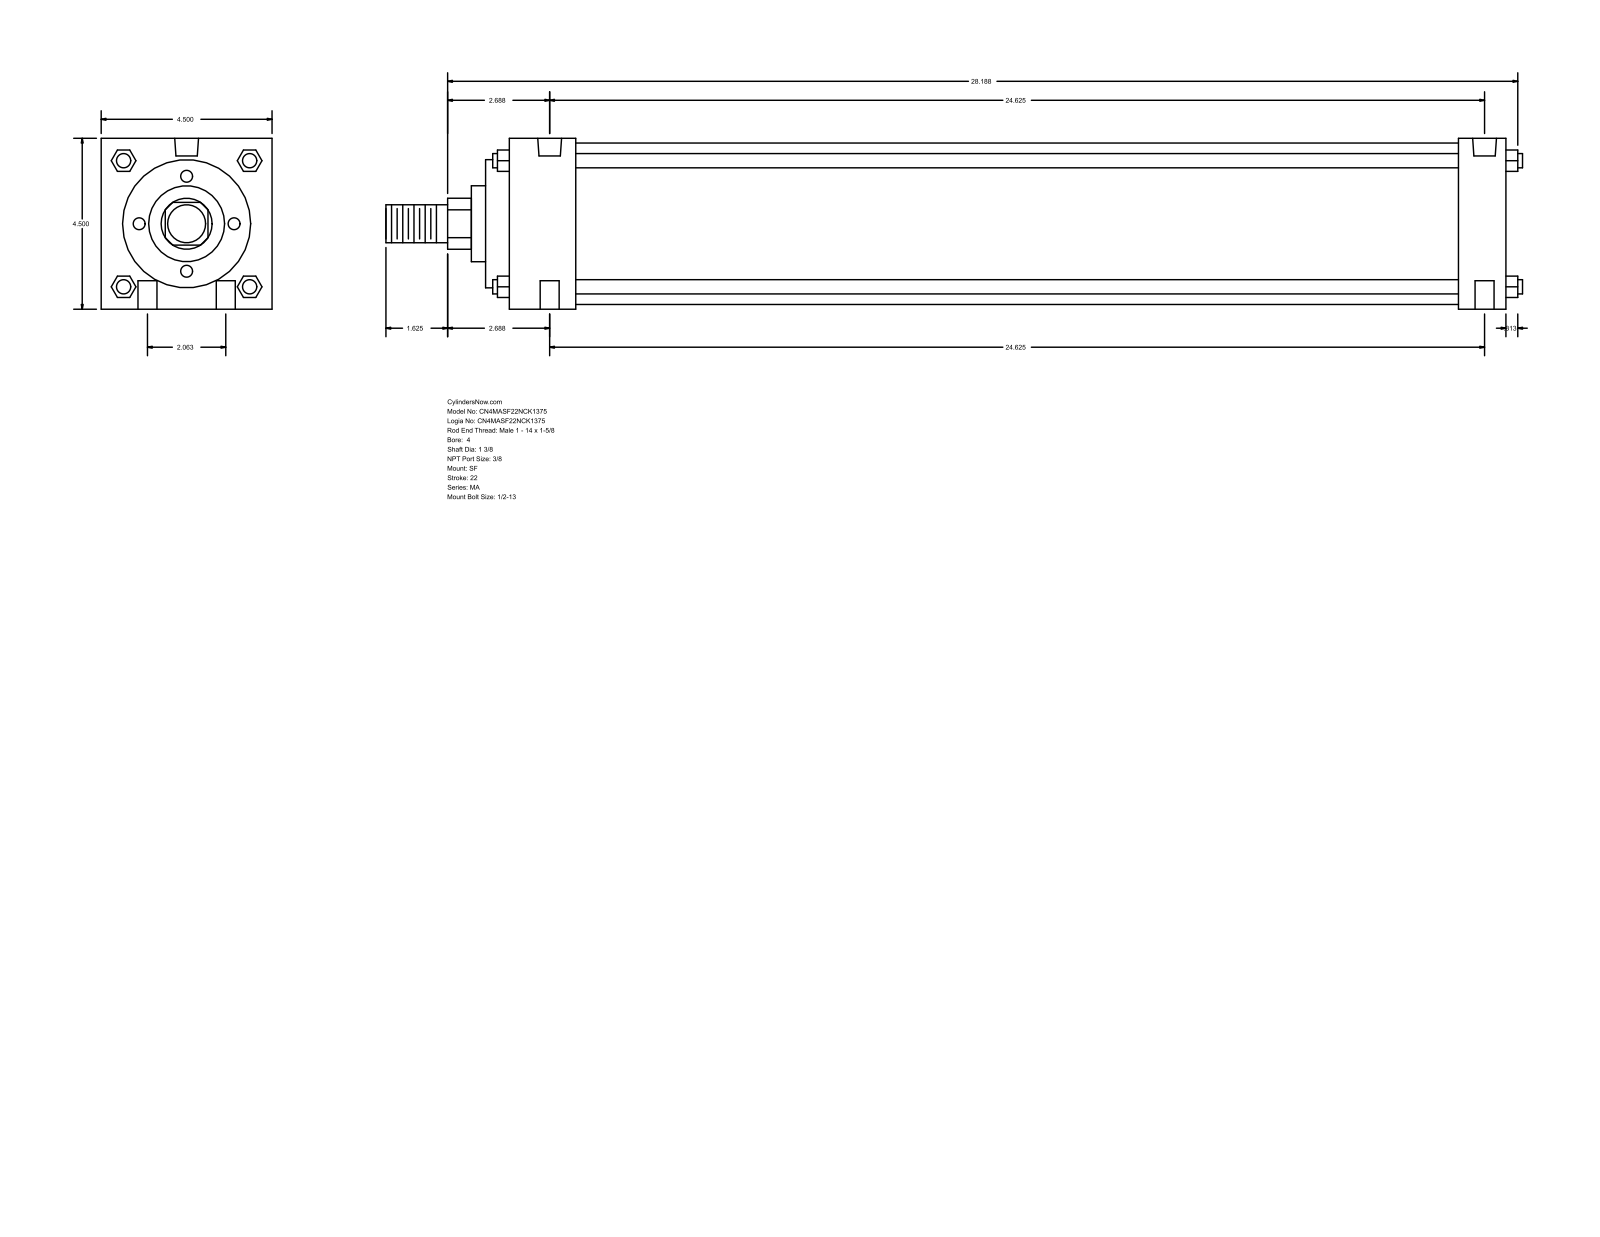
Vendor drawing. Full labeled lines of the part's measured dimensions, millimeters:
Part name (STEP PRODUCT): MA_SF__0400_1.375
STEP written by: GSSL Pune (CONFIG_CONTROL_DESIGN)
Units: millimetres
Bodies: 0 solids, 126 faces (95 planar, 31 cylindrical, 0 other)
Overall size (bounding box): 760.41 × 114.3 × 114.3
Round holes (diameter × count): ⌀12.7 ×4, ⌀11.11 ×2, ⌀15.93 ×2
Round bosses / shafts (diameter × count): ⌀9.53 ×4, ⌀107.95 ×1, ⌀85.72 ×1, ⌀50.8 ×1, ⌀34.92 ×1, ⌀25.4 ×1
Partial cylindrical surfaces — rounded edges, fillets, slot ends (radius × count): R17.06 ×1
Main face-to-face distances: 114.3, 666.75, 682.62, 15.87, 650.87, 635, 31.75, 60.32, 44.45, 590.55
Hole centre spacings: 26.19, 626.03, 625.48, 52.38, 627.67, 615.95
